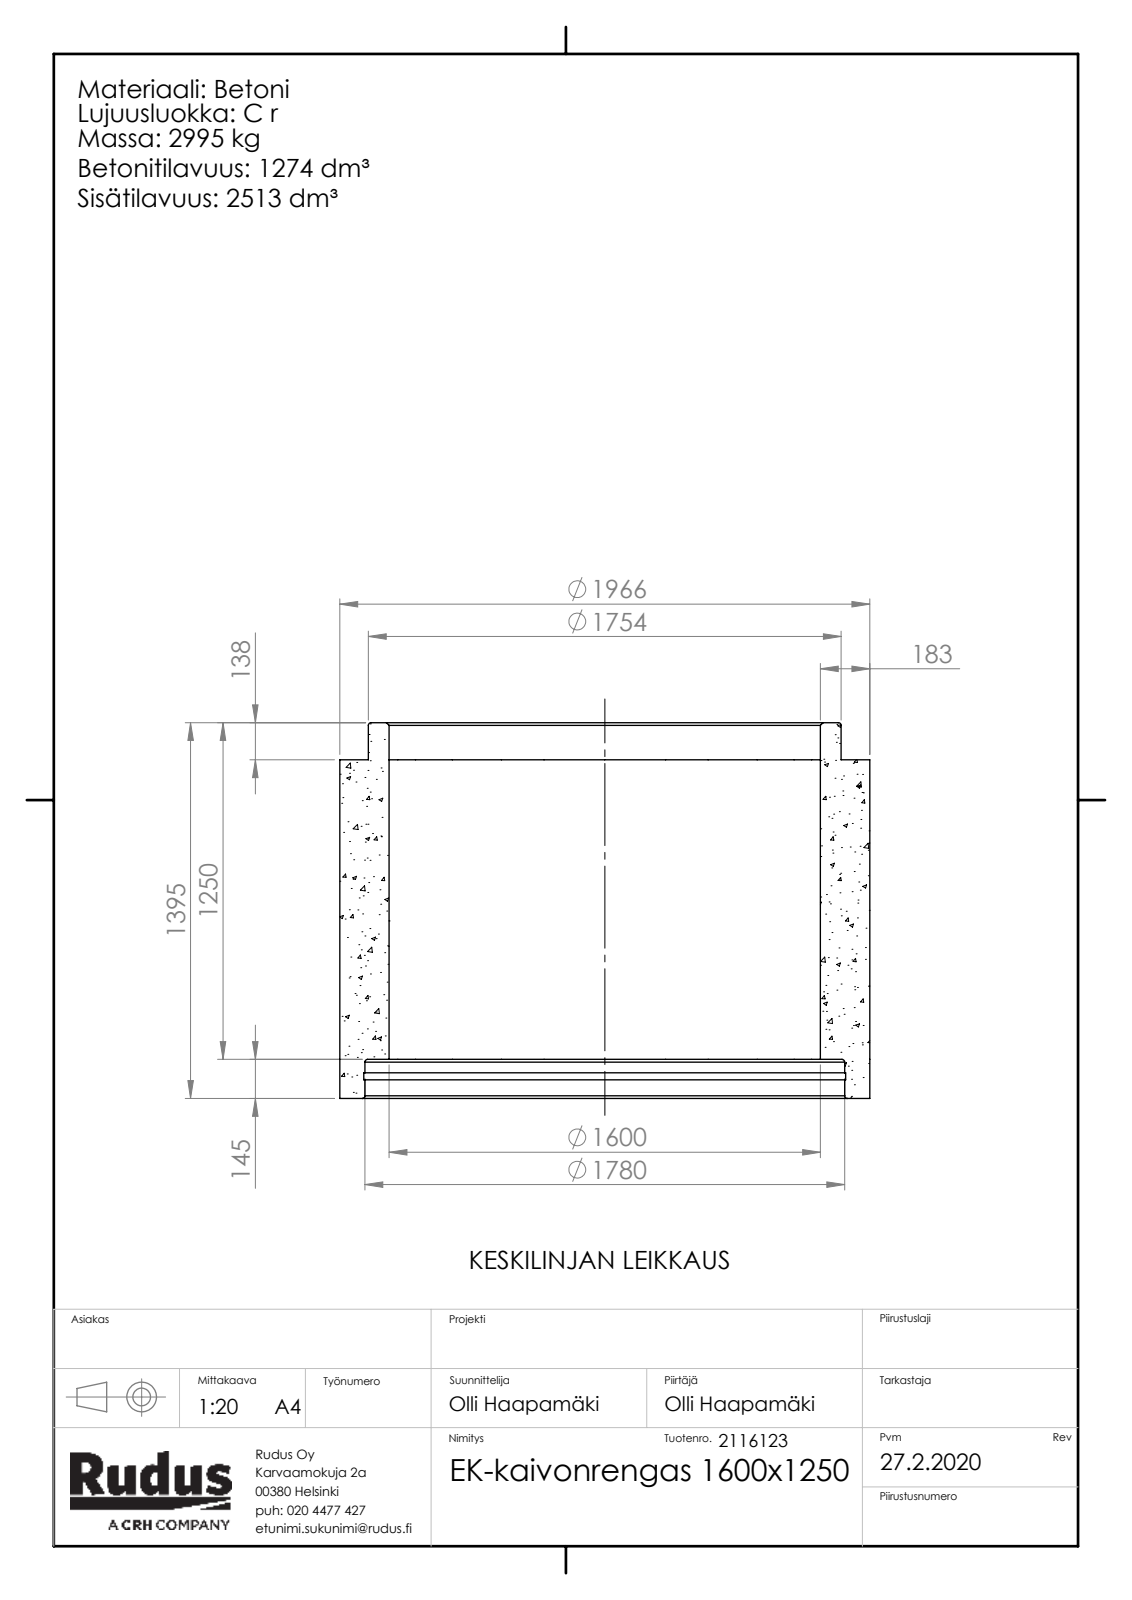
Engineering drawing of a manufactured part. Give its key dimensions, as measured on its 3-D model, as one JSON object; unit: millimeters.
{"part_name": "Rudus 2116123 EK-kaivonrengas 1600x1250; EK-osa-kaivorunko_EK-kaivonrengas", "step_written_by": "SolidWorks 2019 (CONFIG_CONTROL_DESIGN)", "units": "millimeters", "bodies": {"solids": 1, "faces": 107, "planar": 7, "cylindrical": 12, "other": 88}, "overall_size": [1966, 1966, 1395], "volume_mm3": 1275000000, "surface_area_mm2": 17620000, "round_holes": [[1600, 1], [1780, 1], [1788, 1]], "round_bosses_or_shafts": [[1966, 1], [1754.2, 1]], "face_to_face_distances": [1257, 145, 1112, 1395, 1250, 138, 95, 50, 1162, 1300]}
